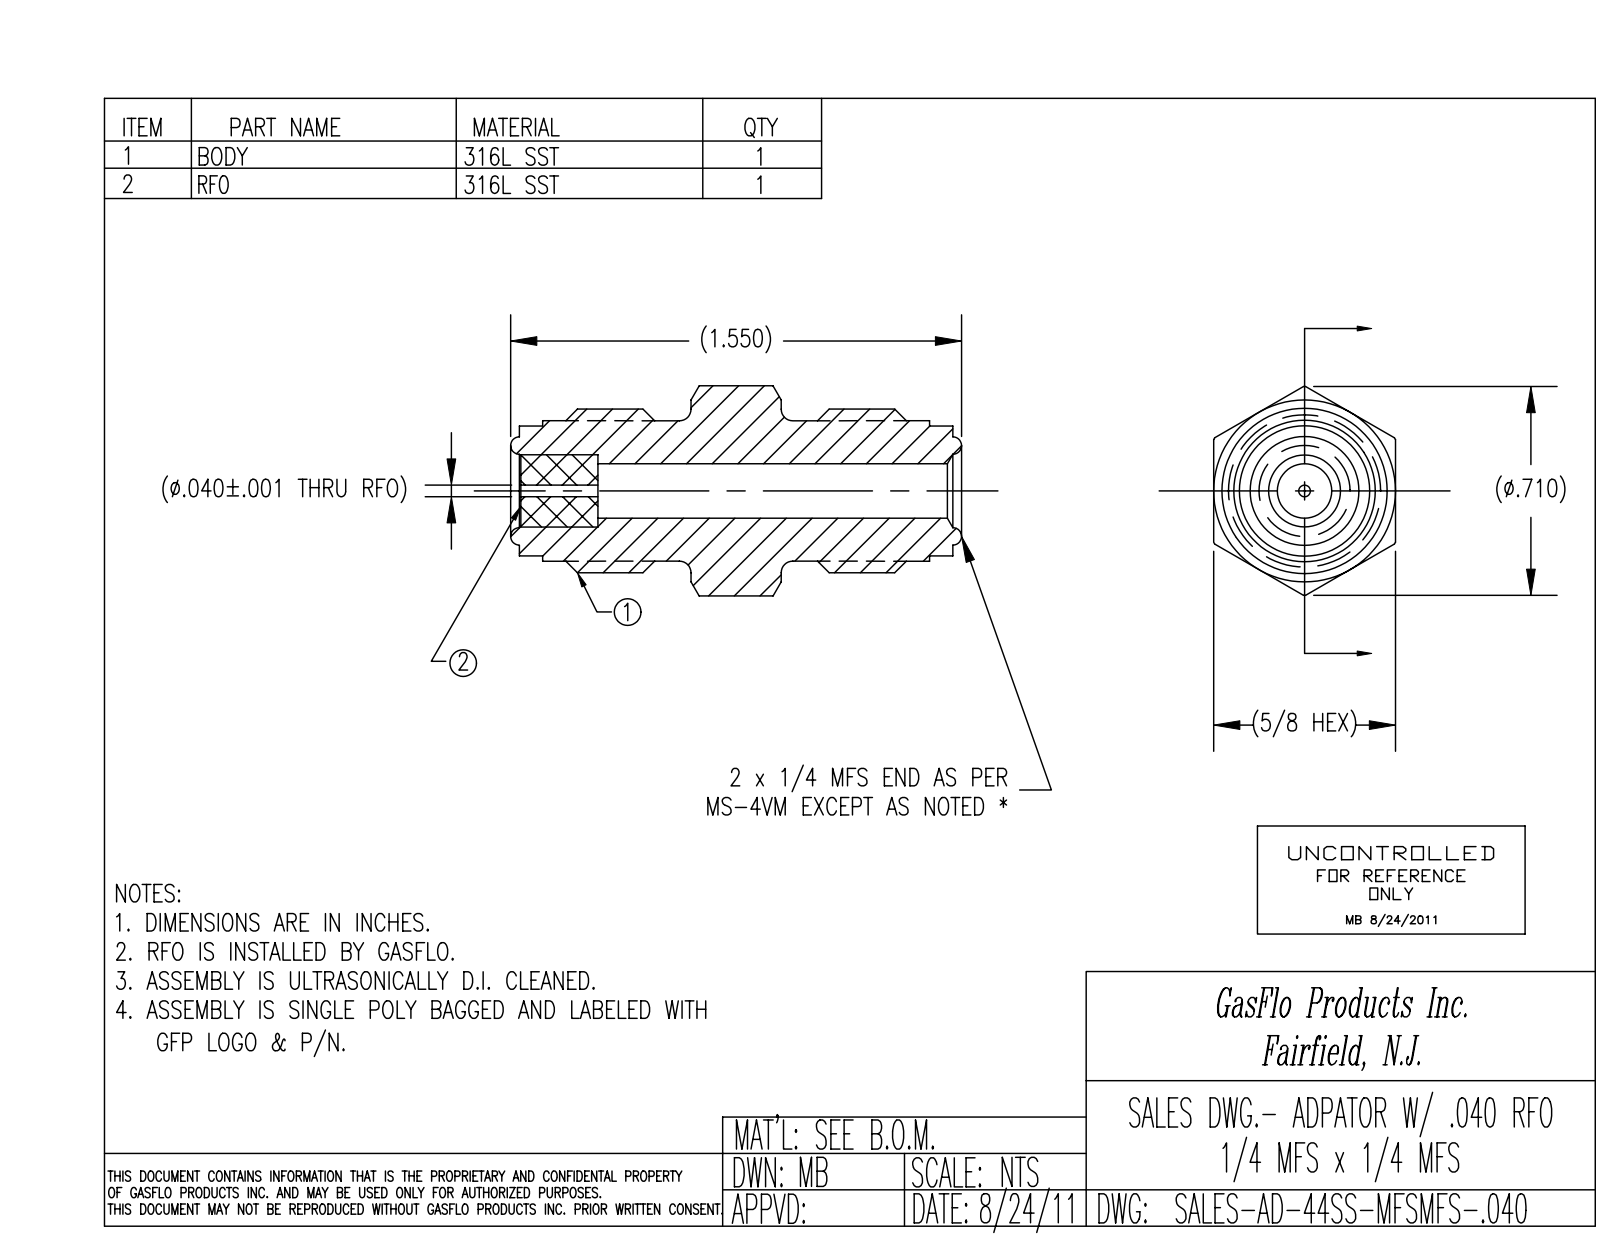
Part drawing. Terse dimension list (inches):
name: PRT-001987; PRT-000431_.040; AD-44SS-MFSMFS-.040
written by: SolidWorks 2018 (CONFIG_CONTROL_DESIGN)
unit: in
bodies: 2 solids, 227 faces (67 planar, 54 cylindrical, 106 other)
size: 1.55 × 0.71 × 0.625
volume: 0.299 in³; area: 5.093 in²
holes: 1× ⌀0.04, 1× ⌀0.125, 1× ⌀0.185, 1× ⌀0.231, 1× ⌀0.248
bosses: 1× ⌀0.557, 1× ⌀0.481, 1× ⌀0.444, 1× ⌀0.393, 1× ⌀0.393, 1× ⌀0.25
rounds: 1× R0.355
face distances: 0.625, 0.62, 0.93, 0.31, 0.109, 1.441, 0.511, 0.82, 1.55, 1.45
